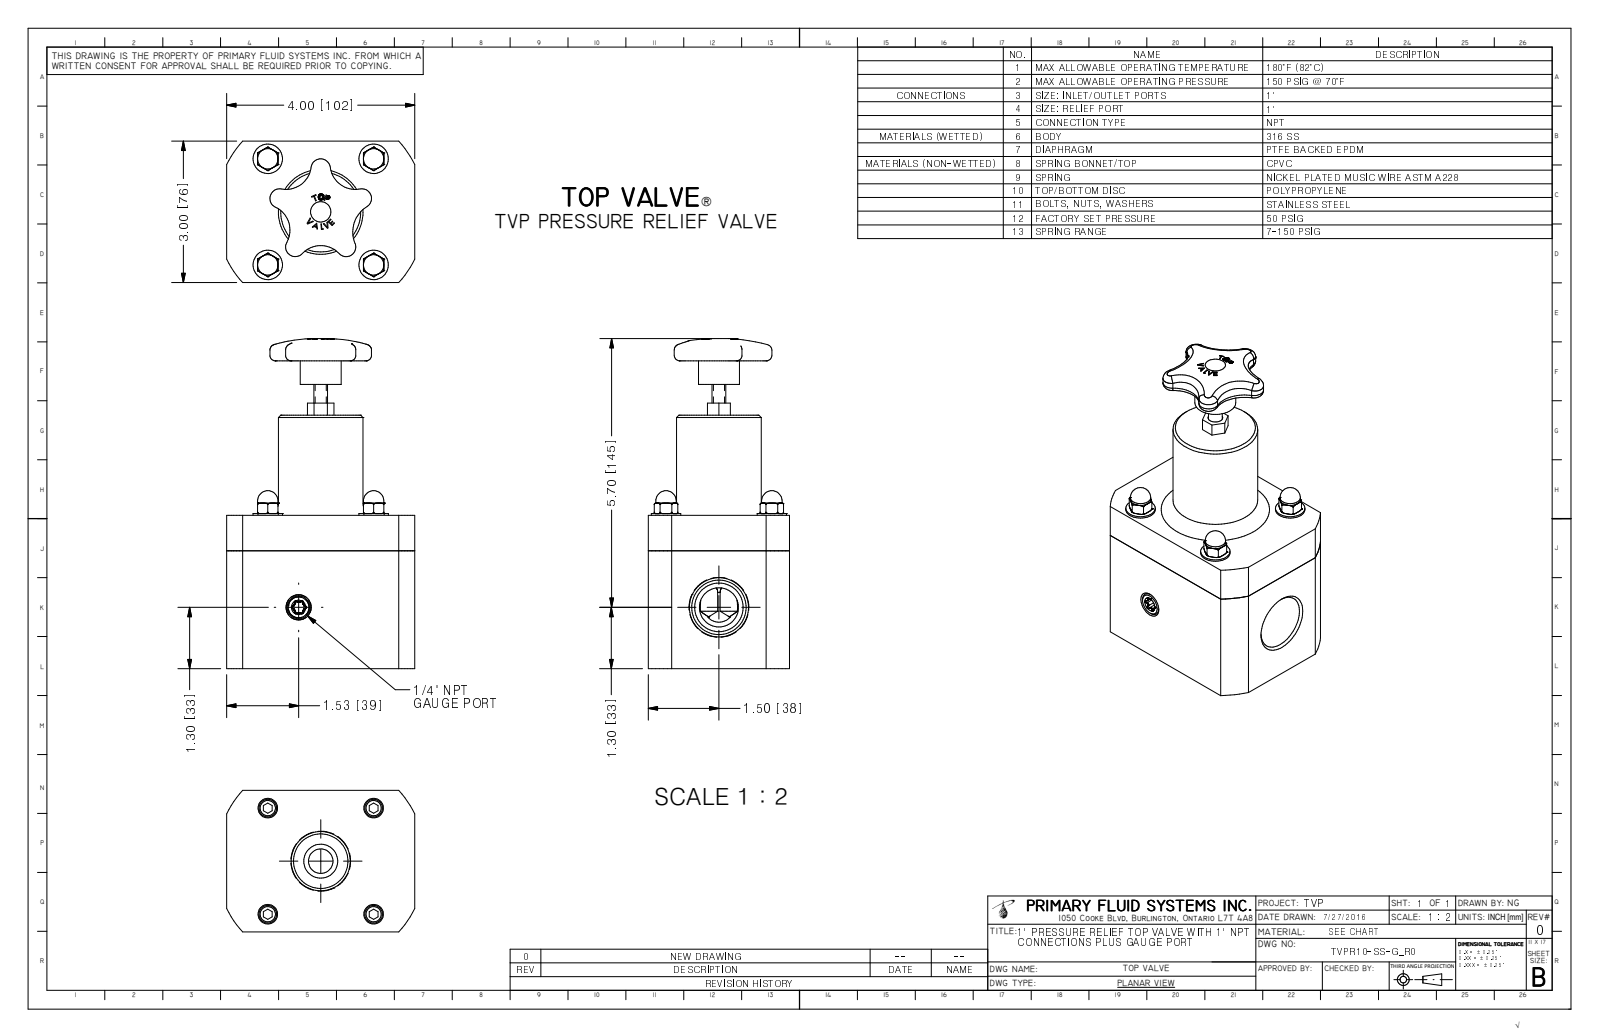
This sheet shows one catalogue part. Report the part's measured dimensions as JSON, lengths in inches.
{"part_name": "TVPR10-SS-G_R0", "step_written_by": "Autodesk Inventor 2009 (AUTOMOTIVE_DESIGN)", "units": "inches", "bodies": {"solids": 1, "faces": 366, "planar": 155, "cylindrical": 54, "other": 157}, "overall_size": [7, 4, 3], "volume_in3": 42.18, "surface_area_in2": 104.5, "round_holes": [[0.175, 4], [1.156, 2], [2.525, 1]], "round_bosses_or_shafts": [[0.625, 4], [0.433, 4], [0.375, 4], [2.5, 1], [1.8, 1], [0.87, 1], [0.293, 1]], "partial_cylinders_radius": [[0.027, 6], [0.085, 5], [0.205, 5], [0.536, 4], [0.656, 4], [0.625, 1], [0.745, 1], [2.238, 1]], "face_to_face_distances": [3, 3.25, 4, 1, 5.375, 2.125, 2, 0.6, 2.65, 4.775], "hole_center_spacings": [2.25, 1.591, 3.182, 1.591, 1.591]}
